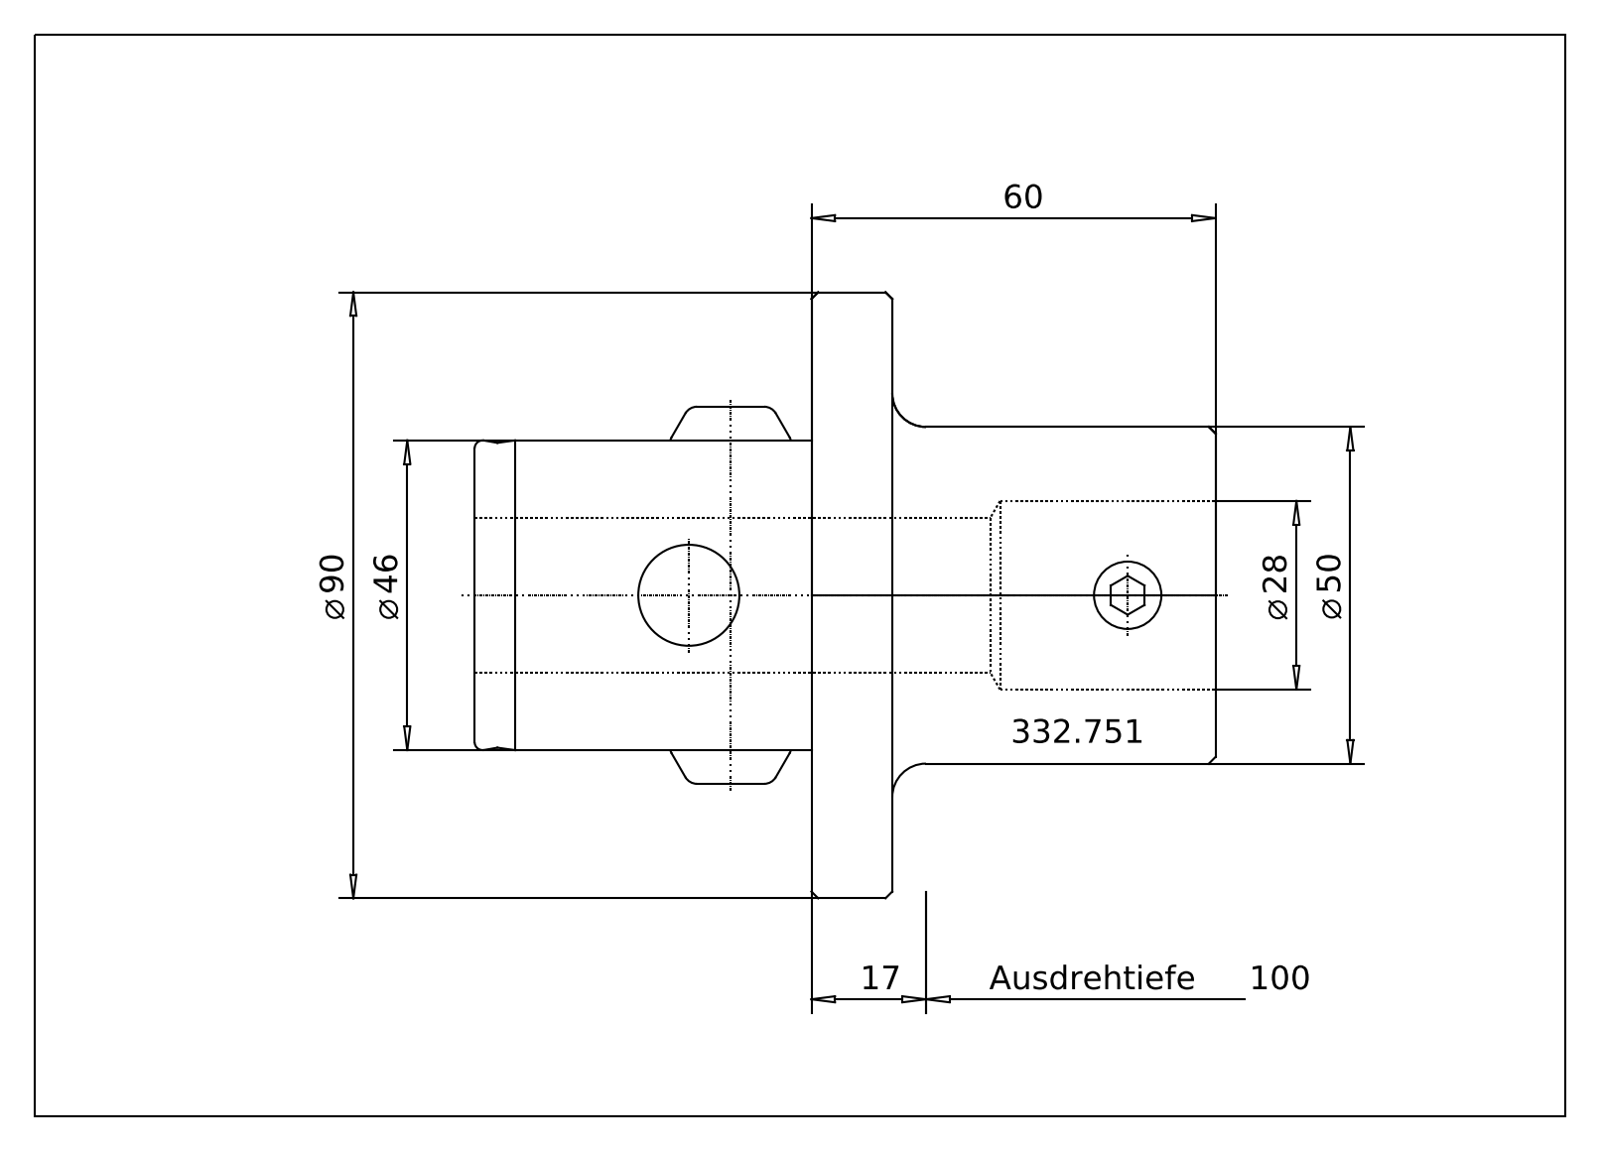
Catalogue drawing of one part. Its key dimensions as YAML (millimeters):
part_name: "332.751 Kaiser CKS7 X CK5 X 100B|690.435 Kaiser ETL M10 X 14 CK5_Standard;NONE; 332.751 Kaiser CKS7 X CK5 X 100B|332.751 Kaiser CKS7 X CK5 X 100B_Standard;NONE; 332.751 Kaiser CKS7 X CK5 X 100B|691.507 Kaiser ETL �18 X 56K_Standard|691.527 Mitnehmerbolzen_Standard;NONE; 332.751 Kaiser CKS7 X CK5 X 100B|691.507 Kaiser ETL �18 X 56K_Standard|693.306 Sprengring_Standard;NONE"
step_written_by: "ACIS (automotive_design)"
units: millimeters
bodies: {solids: 4, faces: 169, planar: 38, cylindrical: 49, other: 82}
overall_size: [110, 90, 90]
volume: 204441
surface_area: 43668
round_holes:
  - {diameter: 7.5, count: 1}
  - {diameter: 8.92, count: 1}
  - {diameter: 10.3, count: 1}
  - {diameter: 15, count: 1}
  - {diameter: 22.1, count: 1}
  - {diameter: 24, count: 1}
  - {diameter: 24.7, count: 1}
  - {diameter: 28, count: 1}
  - {diameter: 28.5, count: 1}
round_bosses_or_shafts:
  - {diameter: 90, count: 1}
  - {diameter: 50, count: 1}
  - {diameter: 48.8, count: 1}
  - {diameter: 46, count: 1}
  - {diameter: 18, count: 1}
  - {diameter: 15, count: 1}
  - {diameter: 12, count: 1}
  - {diameter: 10, count: 1}
partial_cylinders:
  - {radius: 4.5, count: 2}
face_to_face_distances: [11.9, 61.9, 50, 48.1, 60, 110, 5, 24.1, 27.2, 28.8]
hole_center_spacings: [19.5, 65.15]
